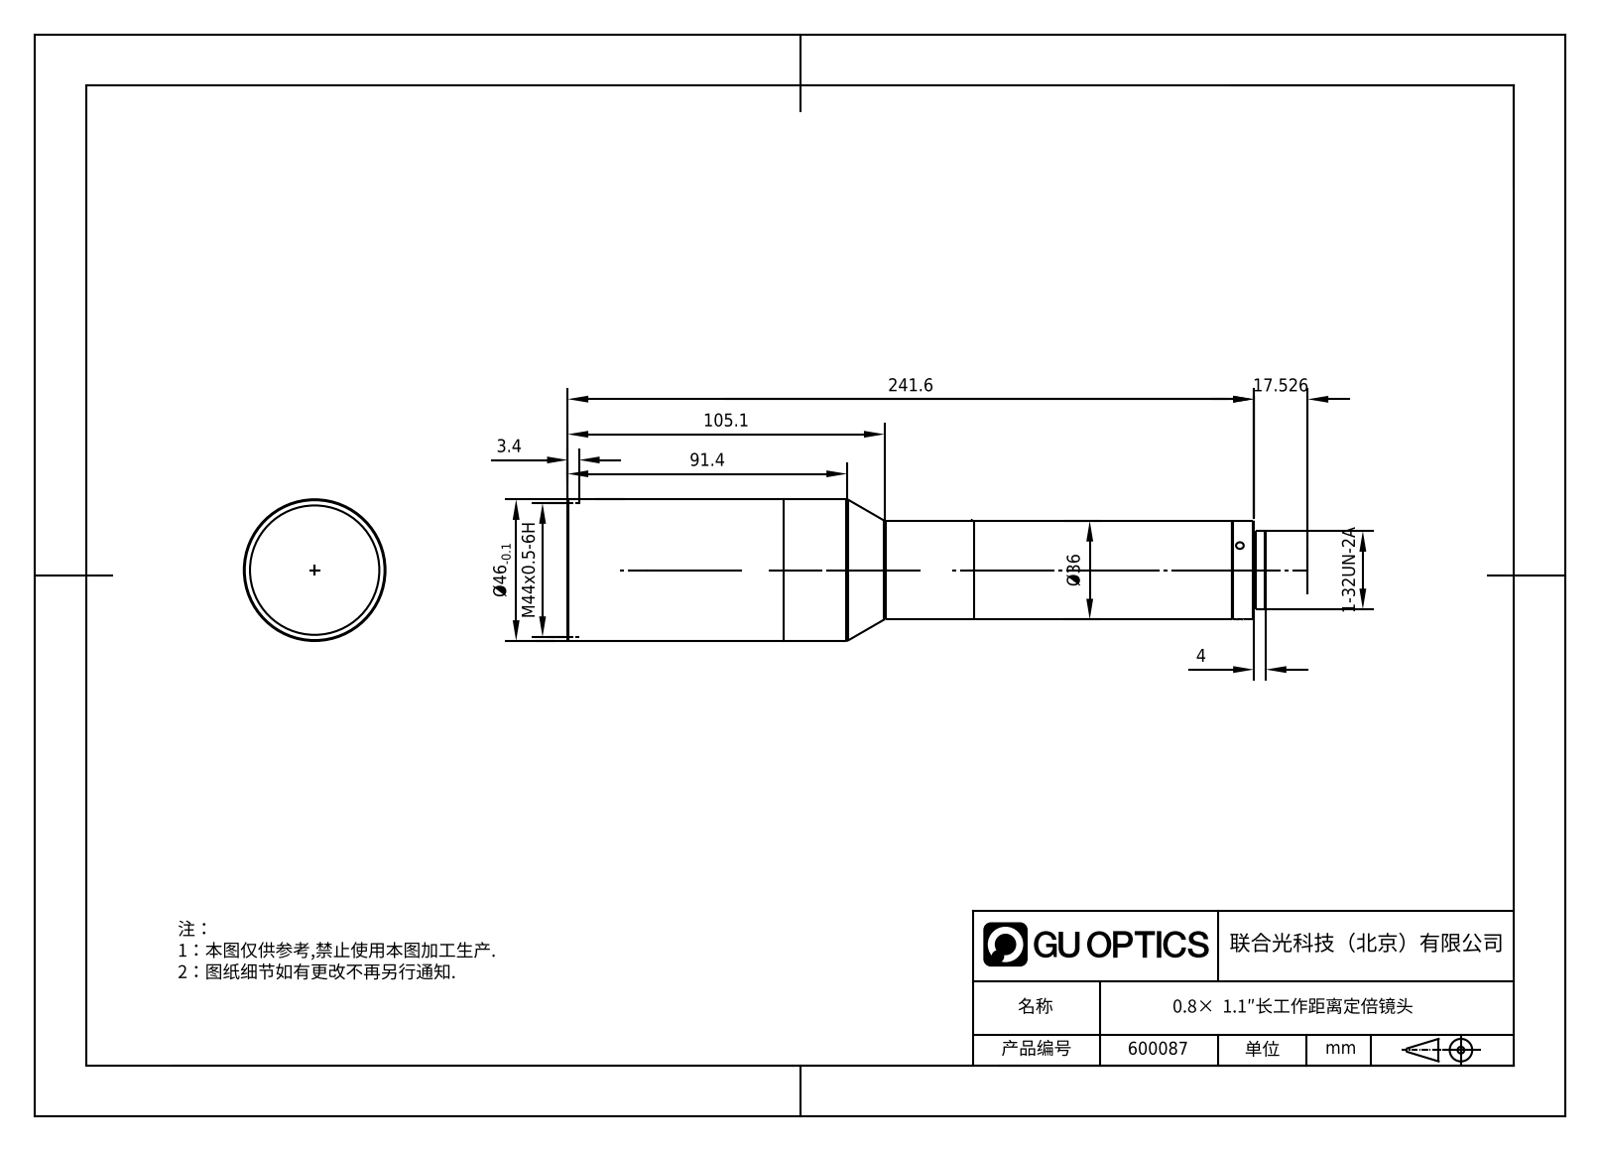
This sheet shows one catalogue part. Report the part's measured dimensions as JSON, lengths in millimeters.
{"part_name": "600087", "step_written_by": "SolidWorks 2020 (CONFIG_CONTROL_DESIGN)", "units": "millimeters", "bodies": {"solids": 2, "faces": 32, "planar": 9, "cylindrical": 14, "other": 9}, "overall_size": [245.59, 46, 46], "volume_mm3": 304966, "surface_area_mm2": 38059, "round_holes": [[2.5, 3], [33.2, 1], [42, 1]], "round_bosses_or_shafts": [[46, 1], [36, 1], [33.18, 1], [25.4, 1], [24.6, 1]], "face_to_face_distances": [232.59, 4, 236.59, 245.59, 241.59, 9, 0.8, 3.2, 233.39, 242.39]}
